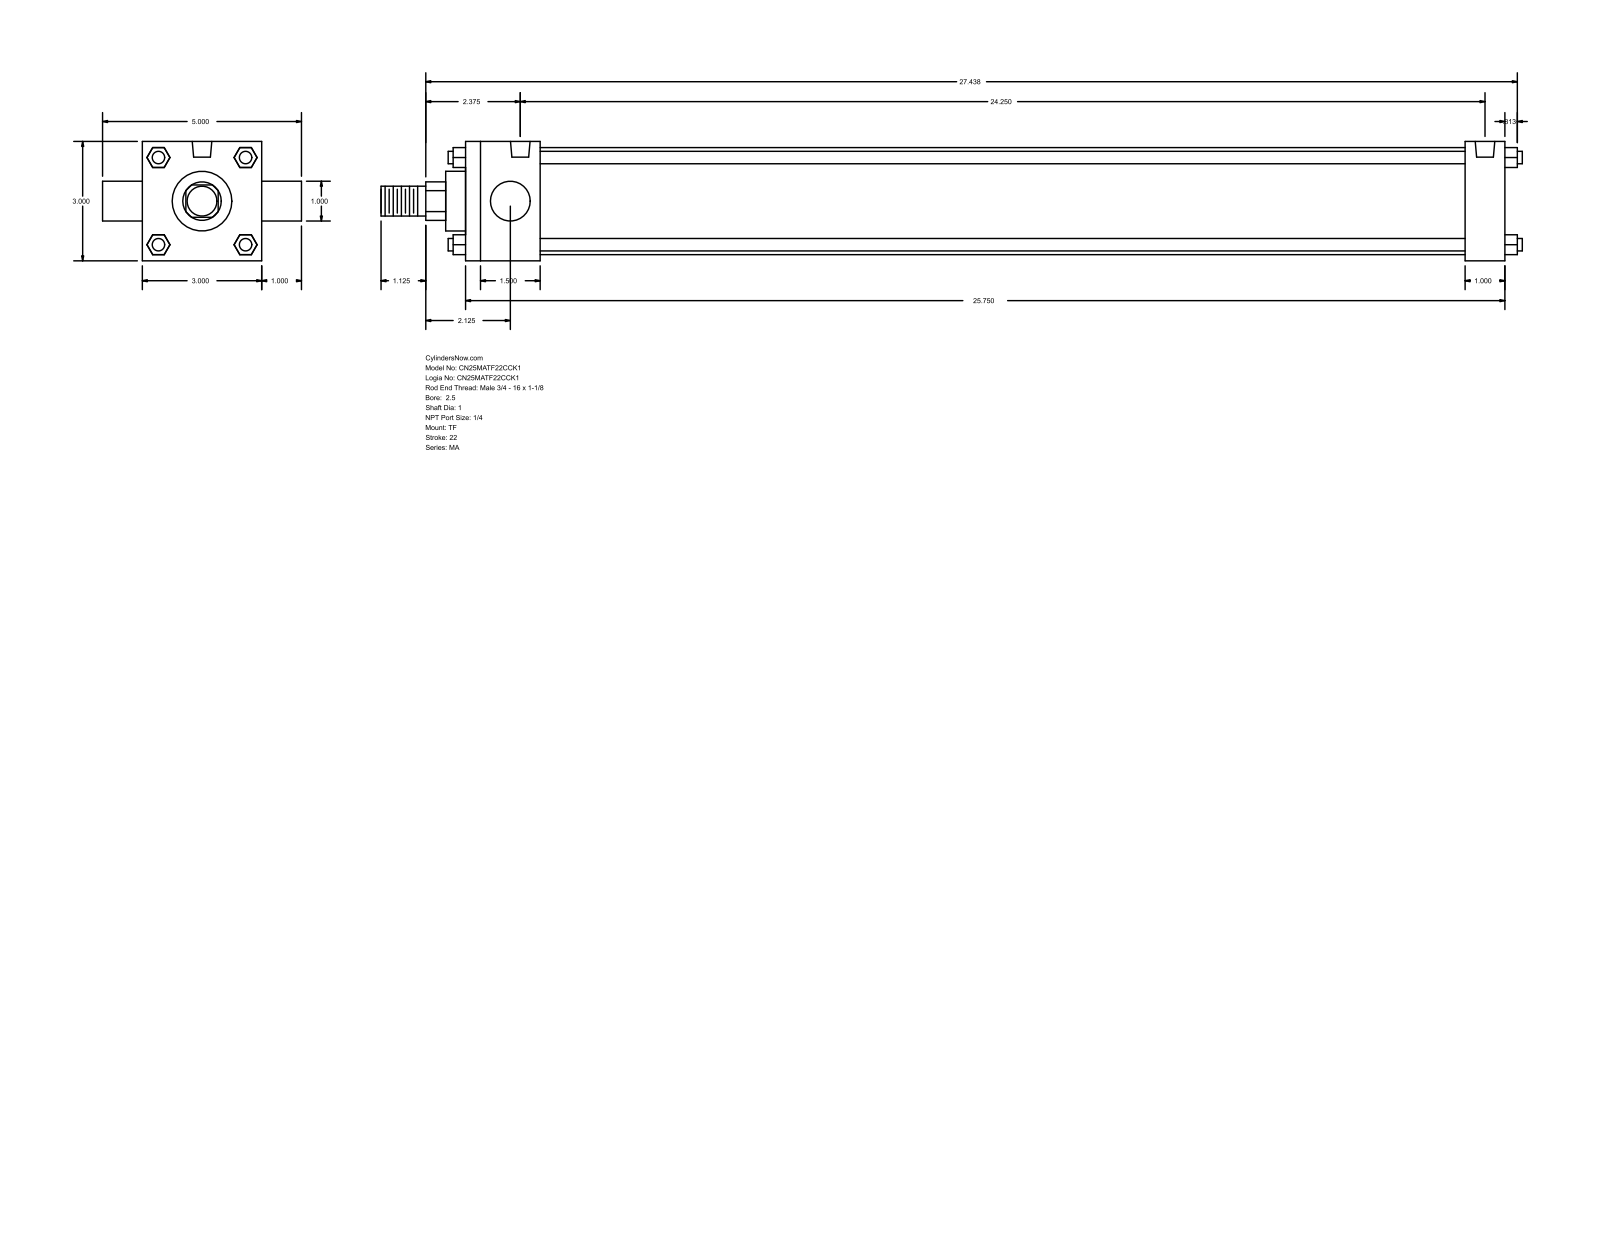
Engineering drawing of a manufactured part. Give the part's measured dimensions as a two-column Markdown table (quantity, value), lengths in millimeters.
| quantity | value |
| --- | --- |
| part name | MA_TF__0250_1 |
| STEP written by | GSSL Pune (CONFIG_CONTROL_DESIGN) |
| units | millimeters |
| bodies | 0 solids, 120 faces (92 planar, 28 cylindrical, 0 other) |
| overall size | 728.66 × 127 × 76.2 |
| round holes (diameter × count) | 7.94 × 3, 12.49 × 2 |
| round bosses / shafts (diameter × count) | 7.94 × 4, 25.4 × 2, 68.33 × 1, 38.1 × 1, 19.05 × 1 |
| partial cylindrical surfaces (radius × count) | 12.29 × 1 |
| main face-to-face distances | 76.2, 663.58, 25.4, 12.7, 47.63, 638.18, 590.55, 615.95, 101.6, 27.81 |
| hole center spacings | 615.94 |
